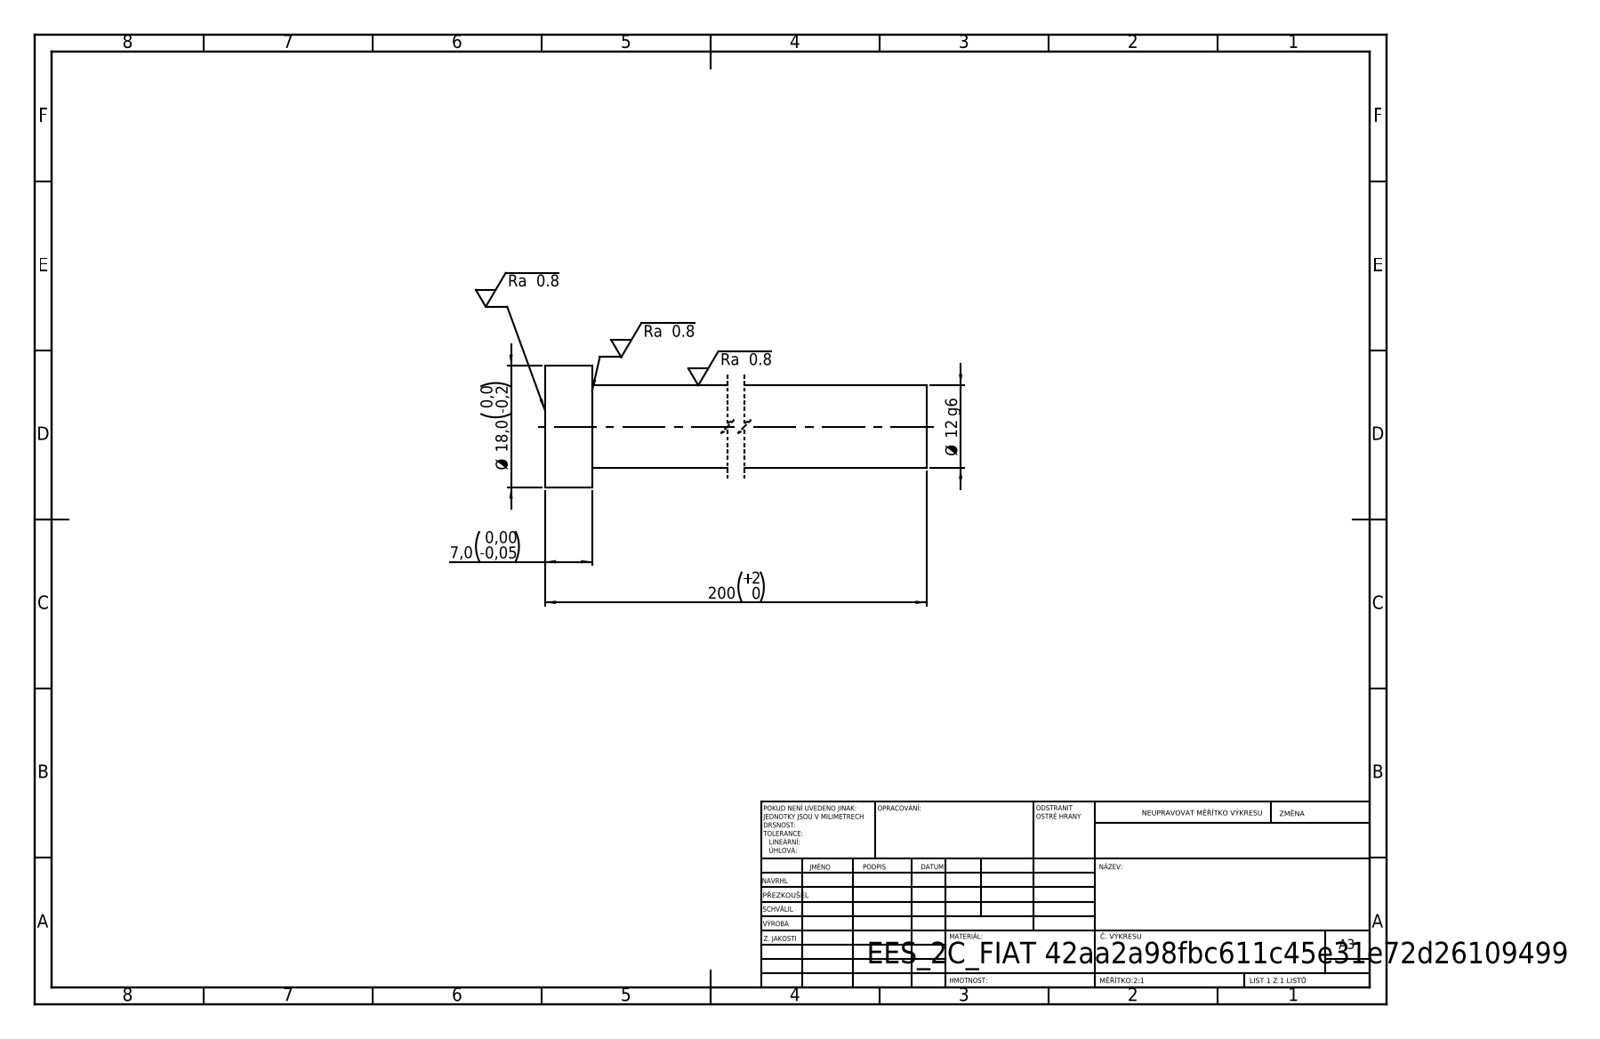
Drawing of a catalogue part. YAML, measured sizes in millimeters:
step_written_by: "SolidWorks 2019 (CONFIG_CONTROL_DESIGN)"
units: millimeters
bodies: {solids: 1, faces: 7, planar: 3, cylindrical: 4, other: 0}
overall_size: [200, 18, 18]
volume: 24343
surface_area: 8302
round_bosses_or_shafts:
  - {diameter: 18, count: 1}
  - {diameter: 12.2, count: 1}
face_to_face_distances: [7, 200, 193]
